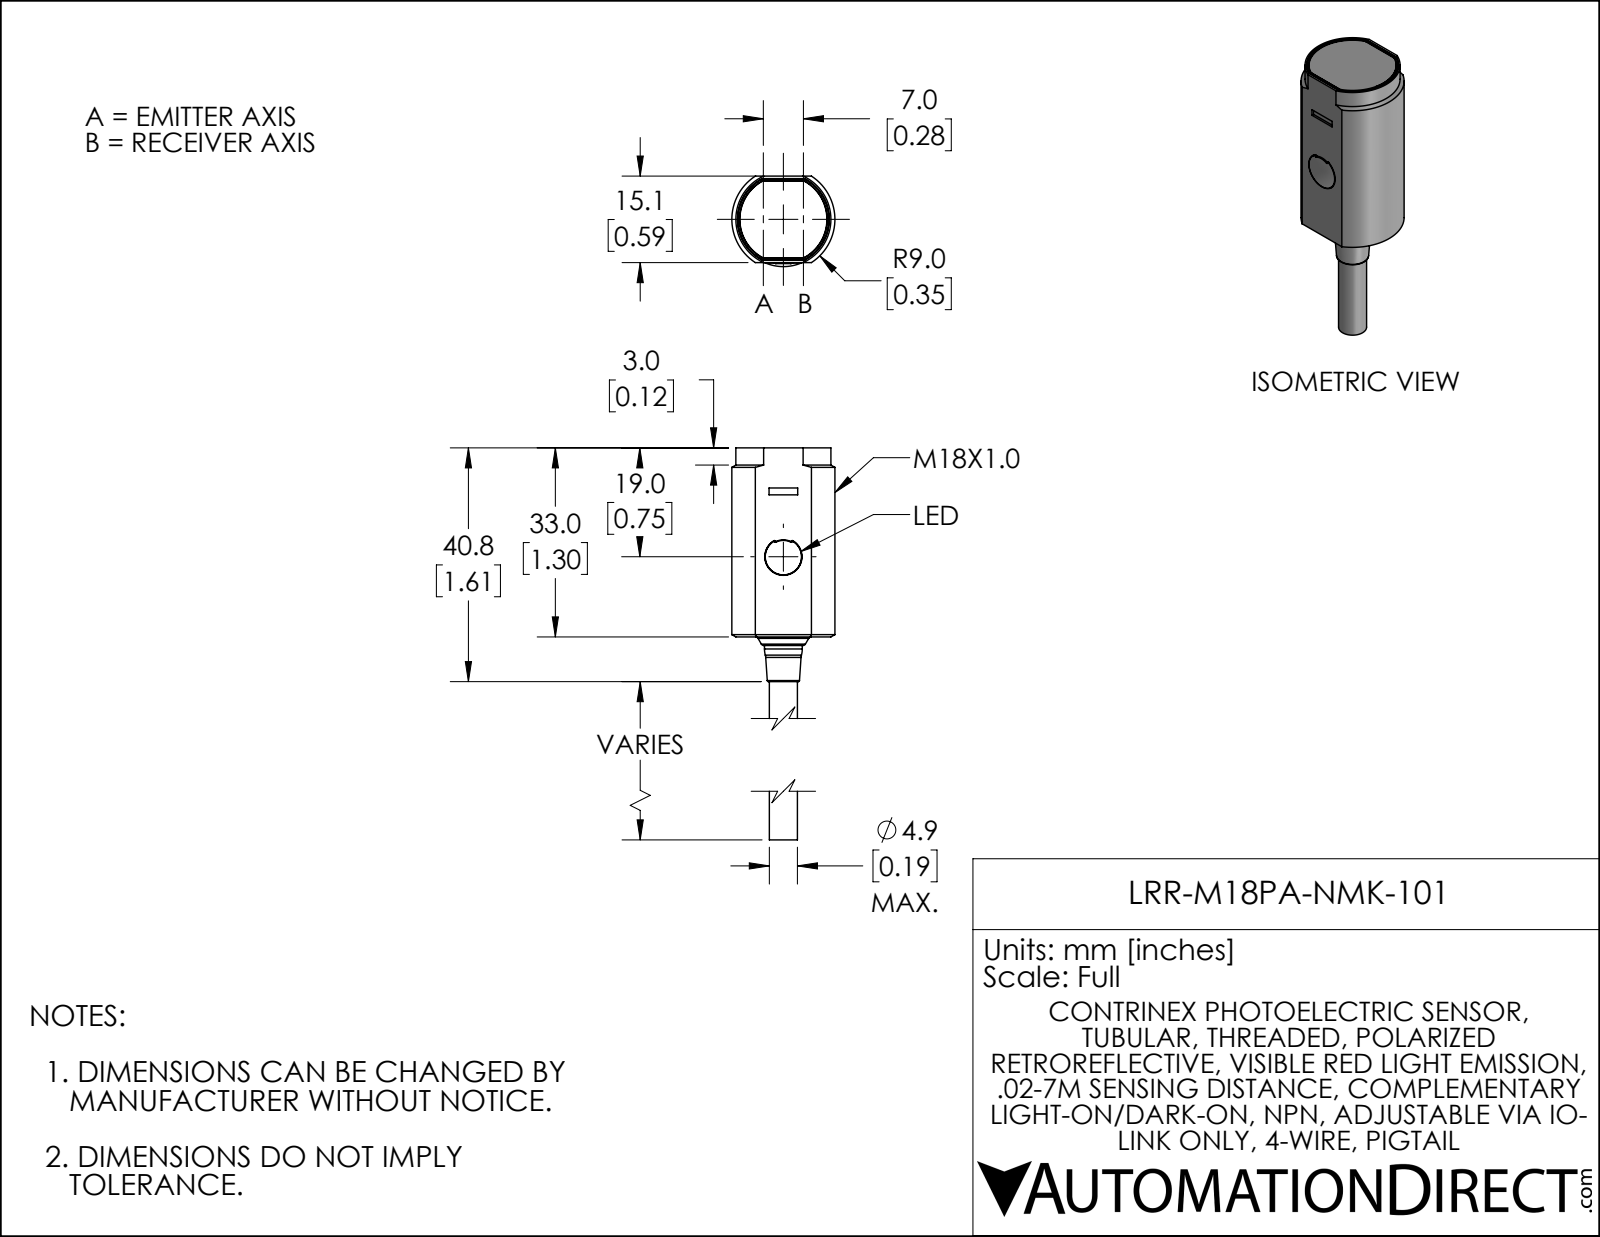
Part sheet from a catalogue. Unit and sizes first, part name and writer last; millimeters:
Units: millimetres
Overall size (bounding box): 56 × 18 × 15.8
Round holes (diameter × count): ⌀6.5 ×1
Round bosses / shafts (diameter × count): ⌀6.6 ×1, ⌀4.9 ×1
Partial cylindrical surfaces — rounded edges, fillets, slot ends (radius × count): R0.2 ×8, R0.4 ×8, R0.7 ×8, R2.8 ×1, R2.9 ×1, R7.6 ×1, R7.7 ×1, R8 ×1
Main face-to-face distances: 15.1, 32.9, 33, 0.4, 56, 56, 23, 14.7, 0.4, 14.3
Volume: 8 210 mm³ · Surface area: 2 729 mm²
Bodies: 1 solid, 93 faces (39 planar, 41 cylindrical, 13 other)
Part name (STEP PRODUCT): LRR-M18PA-NMK-101
STEP written by: SolidWorks 2021 (AUTOMOTIVE_DESIGN)
